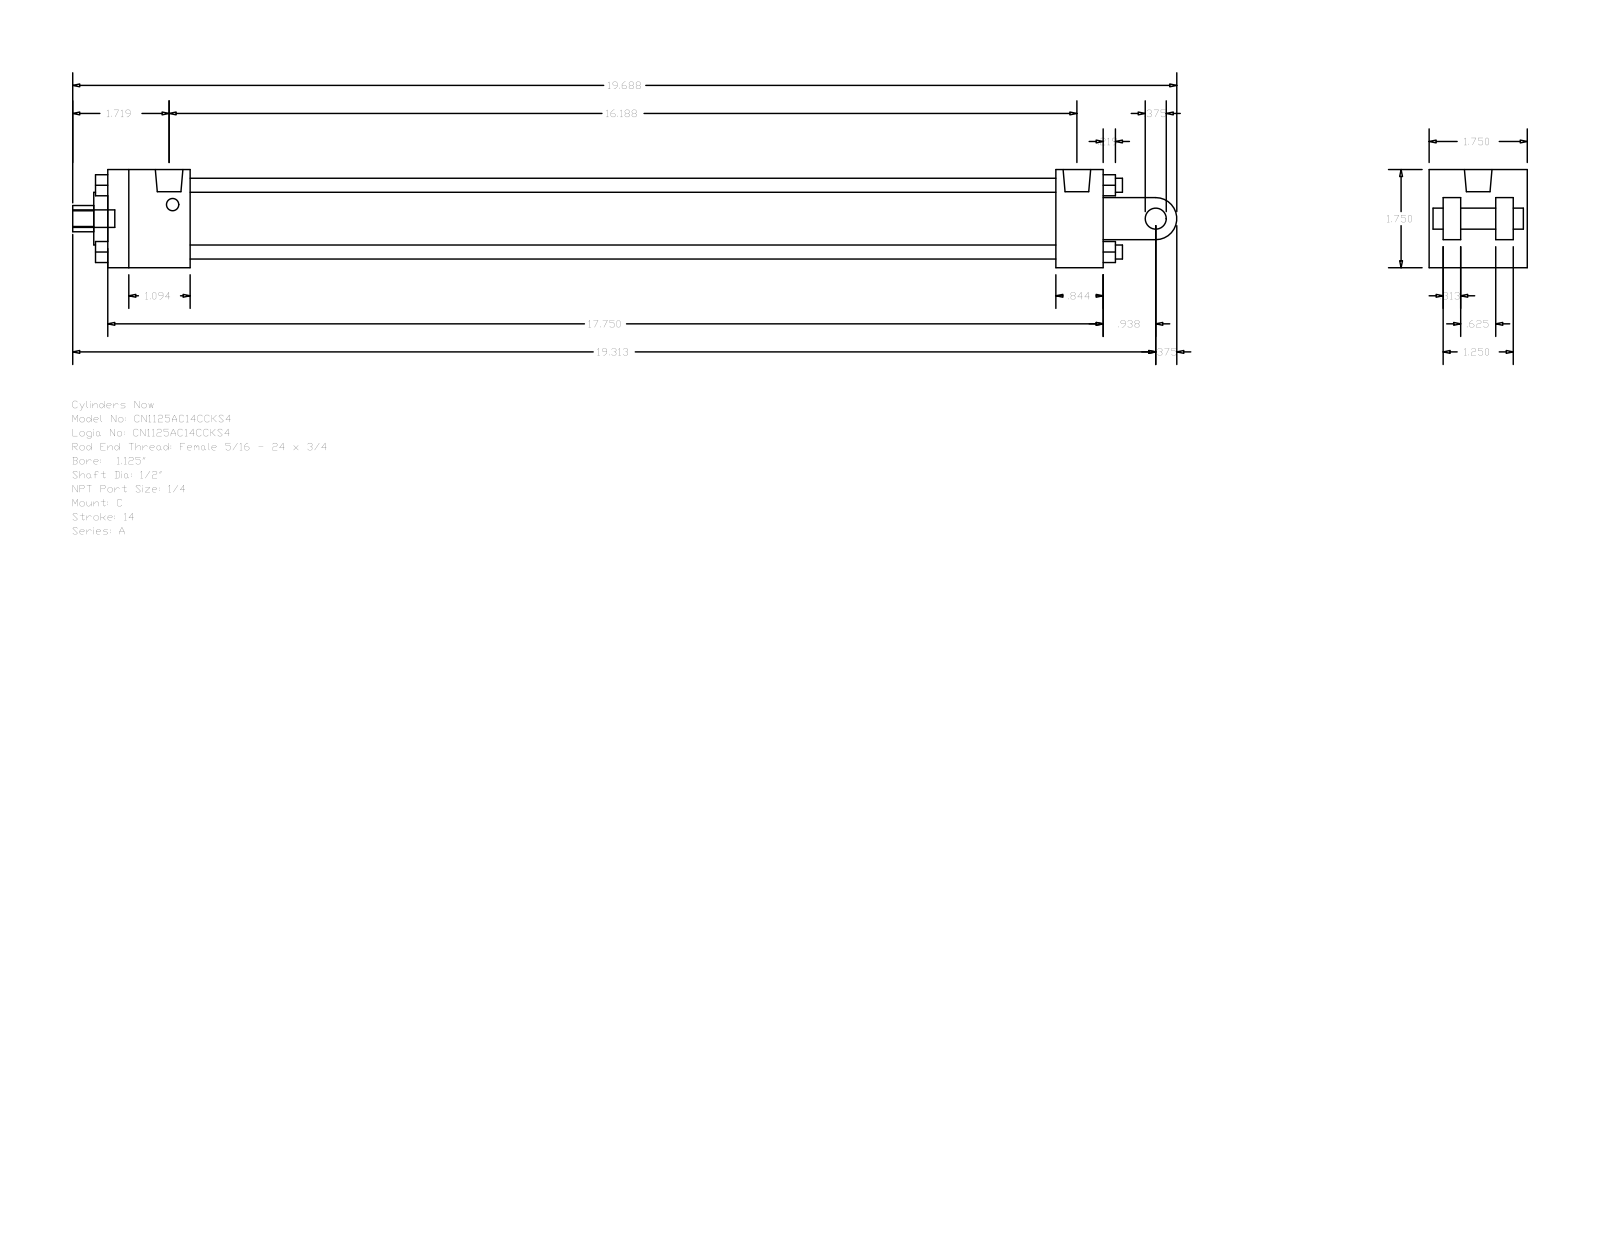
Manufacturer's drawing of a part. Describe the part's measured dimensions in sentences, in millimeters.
The part is named "A_C__0112_0.5". Its 3-D file was written by "GSSL Pune (CONFIG_CONTROL_DESIGN)". It is 0 solids with 135 faces: 102 planar, 33 cylindrical and 0 other. Overall it measures 500.06 by 44.45 by 44.45 millimeters. Round holes: 2 of diameter 5.56, 1 of diameter 12.49, 1 of diameter 12.7, 1 of diameter 23.81, 1 of diameter 31.88. Round bosses or shafts: 4 of diameter 6.35, 2 of diameter 5.56, 1 of diameter 12.49, 1 of diameter 9.53, 1 of diameter 7.94. Partial cylindrical surfaces (rounded edges, fillets, slot ends): 1 of radius 5.94, 1 of radius 9.53. The main face-to-face distances are 44.46, 6.35, 31.76, 14.29, 450.85, 30.17, 429.41, 21.44, 37.3, 392.11. The hole center spacings are 1.59.
